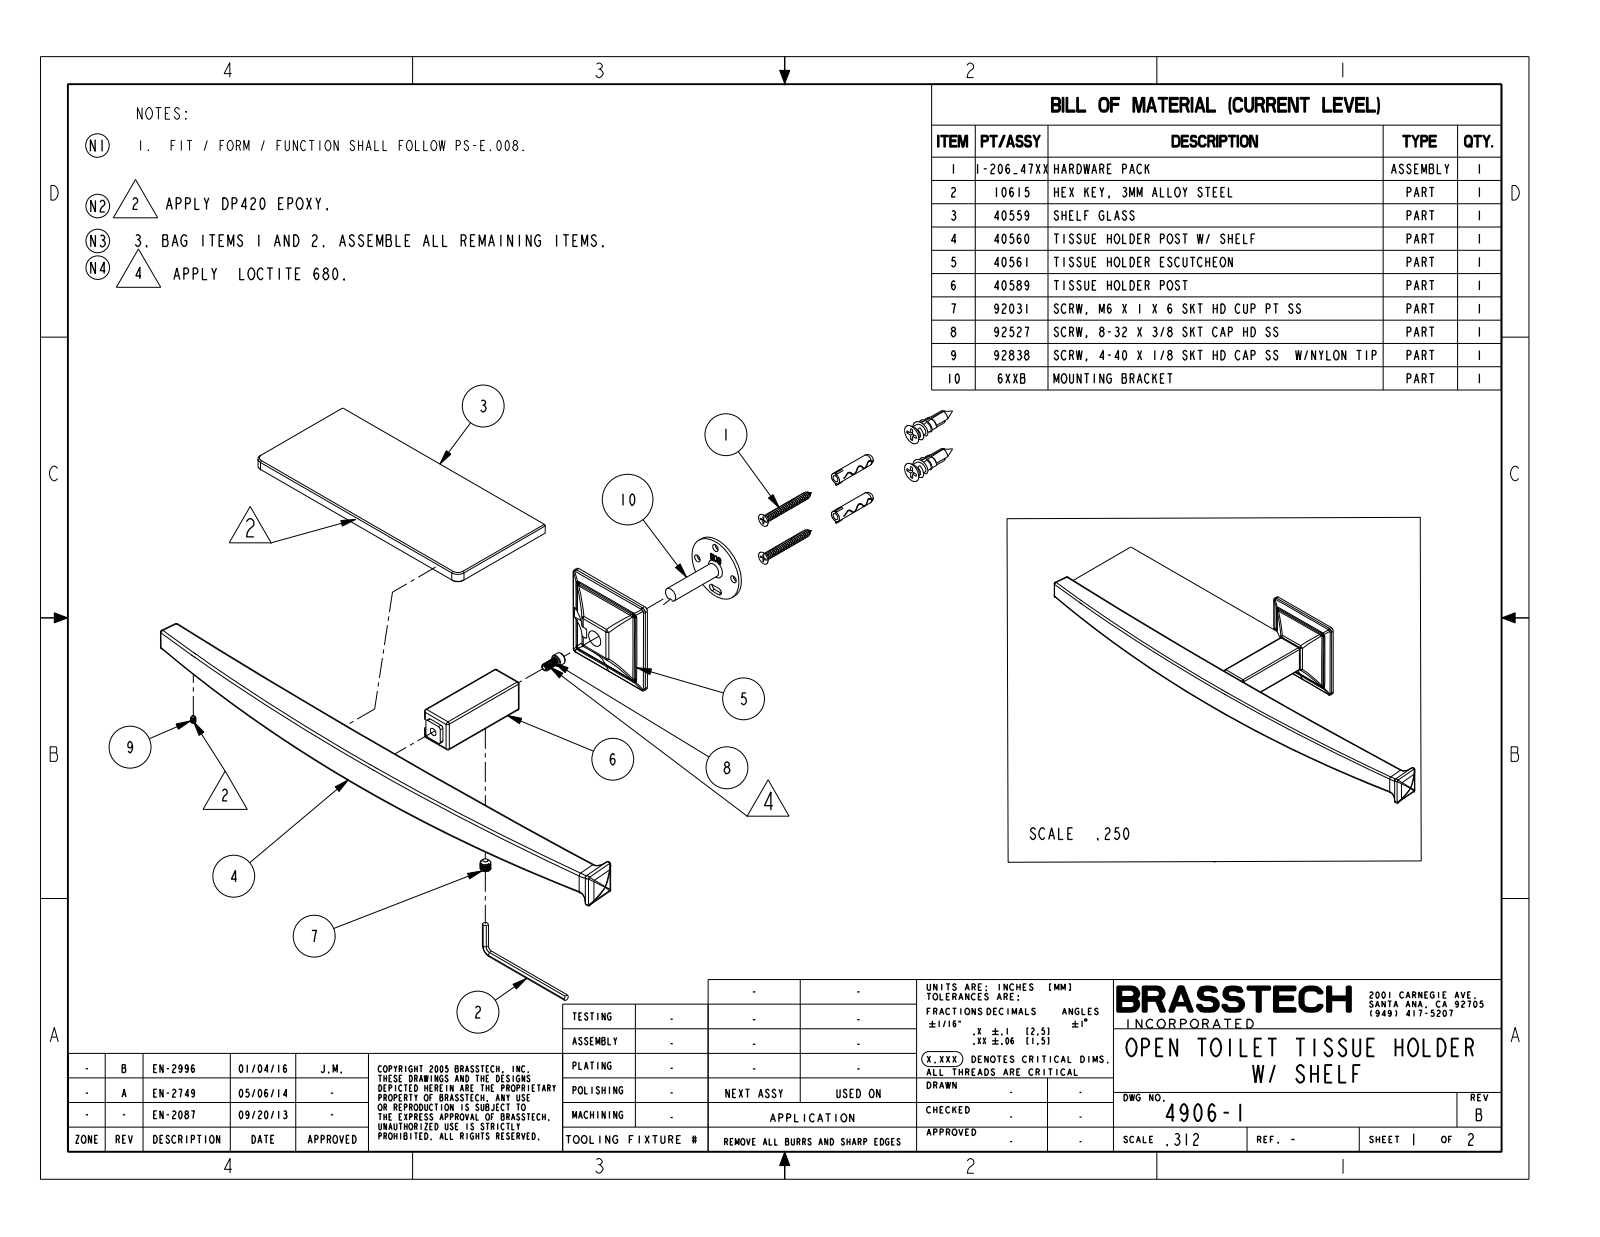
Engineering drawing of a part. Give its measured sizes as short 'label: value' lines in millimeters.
name: 4906-1
written by: PRO/ENGINEER BY PARAMETRIC TECHNOLOGY CORPORATION, 2012230 (CONFIG_CONTROL_DESIGN)
unit: mm
bodies: 0 solids, 309 faces (42 planar, 37 cylindrical, 230 other)
size: 349.1 × 89.7 × 56.5
holes: 3× ⌀4.3, 2× ⌀9.5, 1× ⌀38.1
rounds: 6× R1, 4× R1.3, 4× R2.3, 4× R12.2, 2× R2.2, 1× R4.8, 1× R30.8, 1× R45.4
face distances: 6.4, 74.2, 2.5, 6.3, 71.7, 6.6, 6.6, 2, 0.5, 72.2
hole spacings: 20.2, 14.3, 14.3, 28.6, 28.6, 28.6
